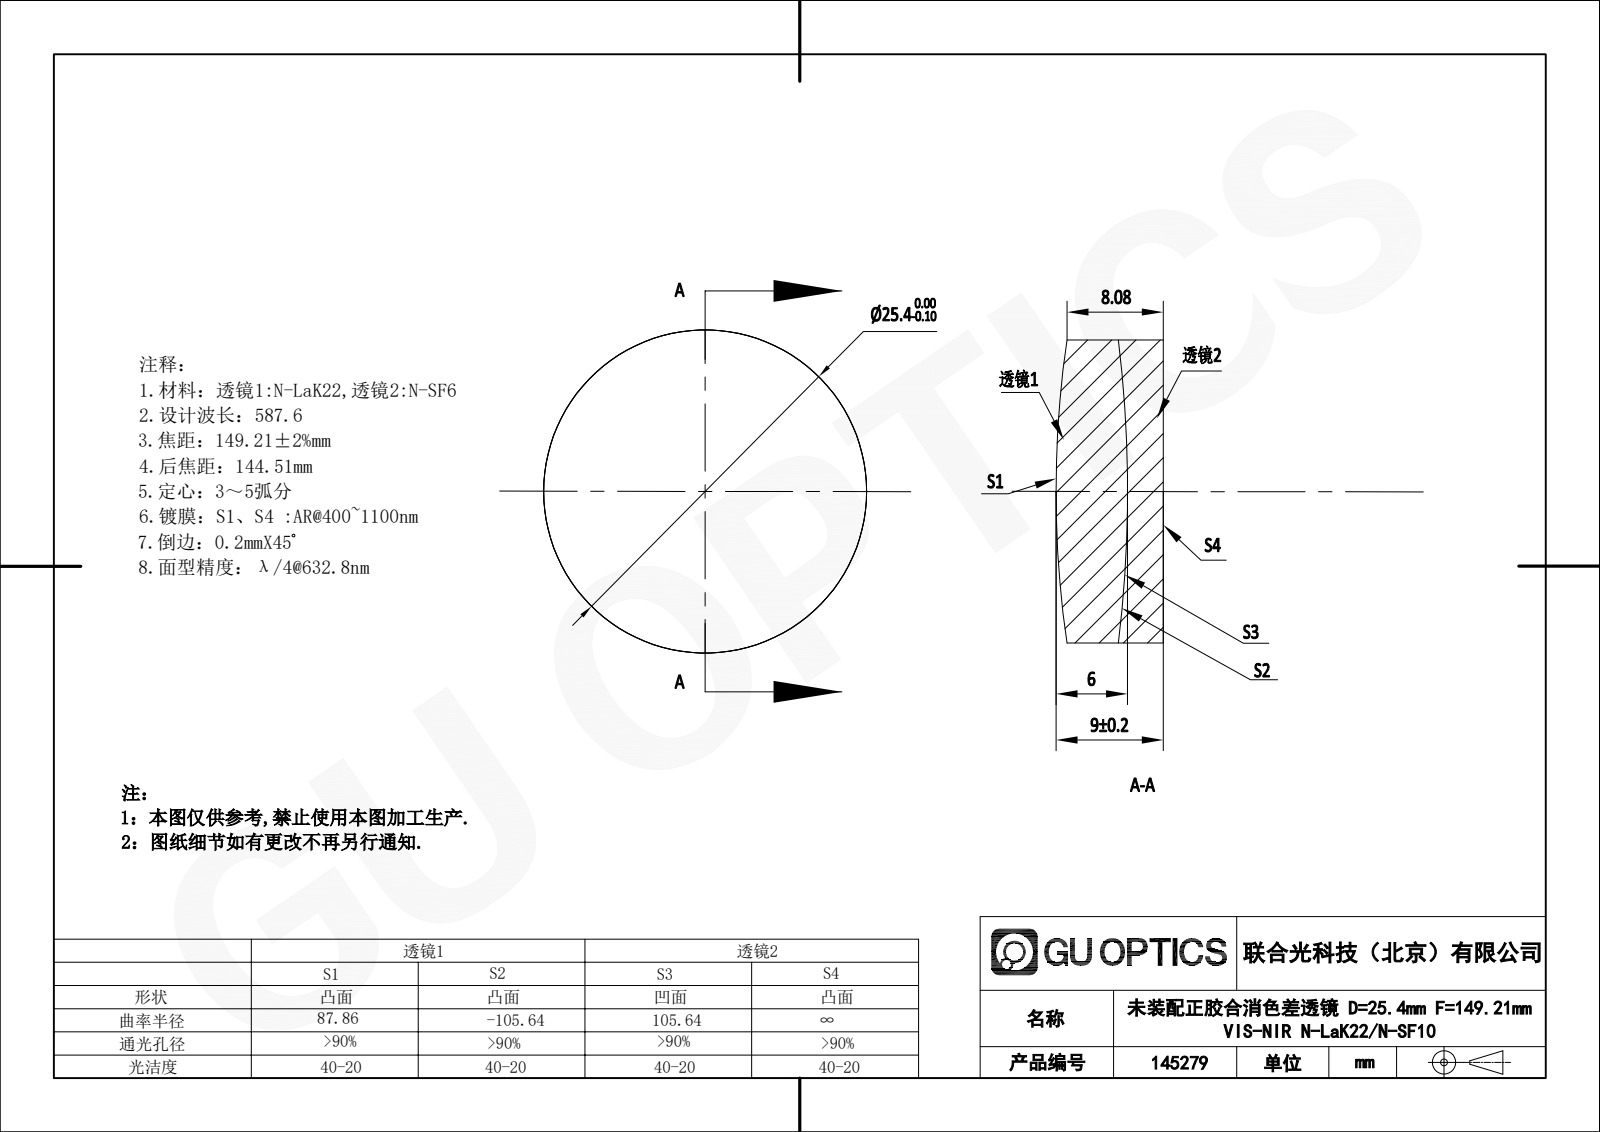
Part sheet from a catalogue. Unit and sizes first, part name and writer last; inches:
Units: inches
Overall size (bounding box): 1 × 1 × 0.354
Round bosses / shafts (diameter × count): ⌀1 ×1
Volume: 0.264 in³ · Surface area: 4.151 in²
Bodies: 2 solids, 11 faces (1 planar, 4 cylindrical, 6 other)
Part name (STEP PRODUCT): 145279
STEP written by: SolidWorks 2020 (CONFIG_CONTROL_DESIGN)
